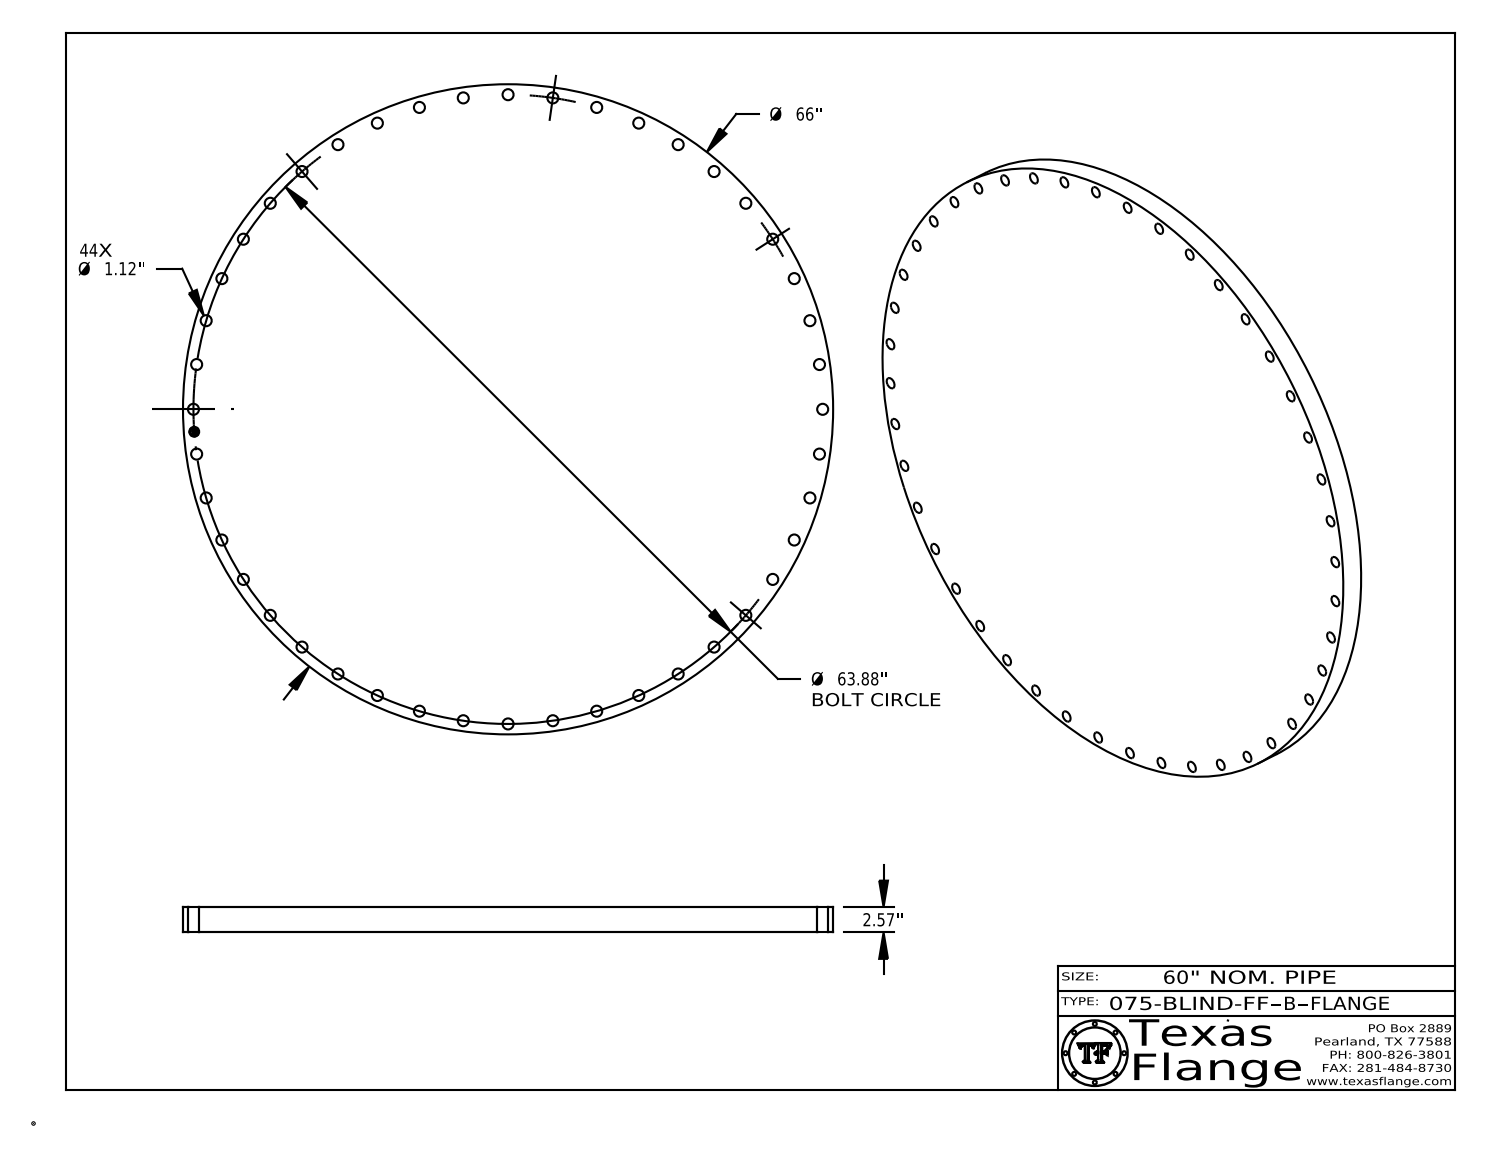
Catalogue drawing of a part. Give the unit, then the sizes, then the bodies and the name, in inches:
Units: inches
Overall size (bounding box): 66 × 66 × 2.57
Round holes (diameter × count): ⌀1.12 ×44, ⌀1 ×1
Round bosses / shafts (diameter × count): ⌀0.061 ×8, ⌀66 ×1, ⌀0.788 ×1
Main face-to-face distances: 2.57, 2.555, 0.015, 0.298, 0.293, 0.054, 0.193, 0.248, 0.044, 0.15
Hole centre spacings: 9.091, 13.579, 63.717, 4.557, 26.537, 38.282, 59.852, 61.293
Volume: 8 681 in³ · Surface area: 7 687 in²
Bodies: 1 solid, 477 faces (367 planar, 110 cylindrical, 0 other)
Part name (STEP PRODUCT): 075-BLIND-FF, Series B
STEP written by: CATIA V5 STEP AP214 (AUTOMOTIVE_DESIGN)
